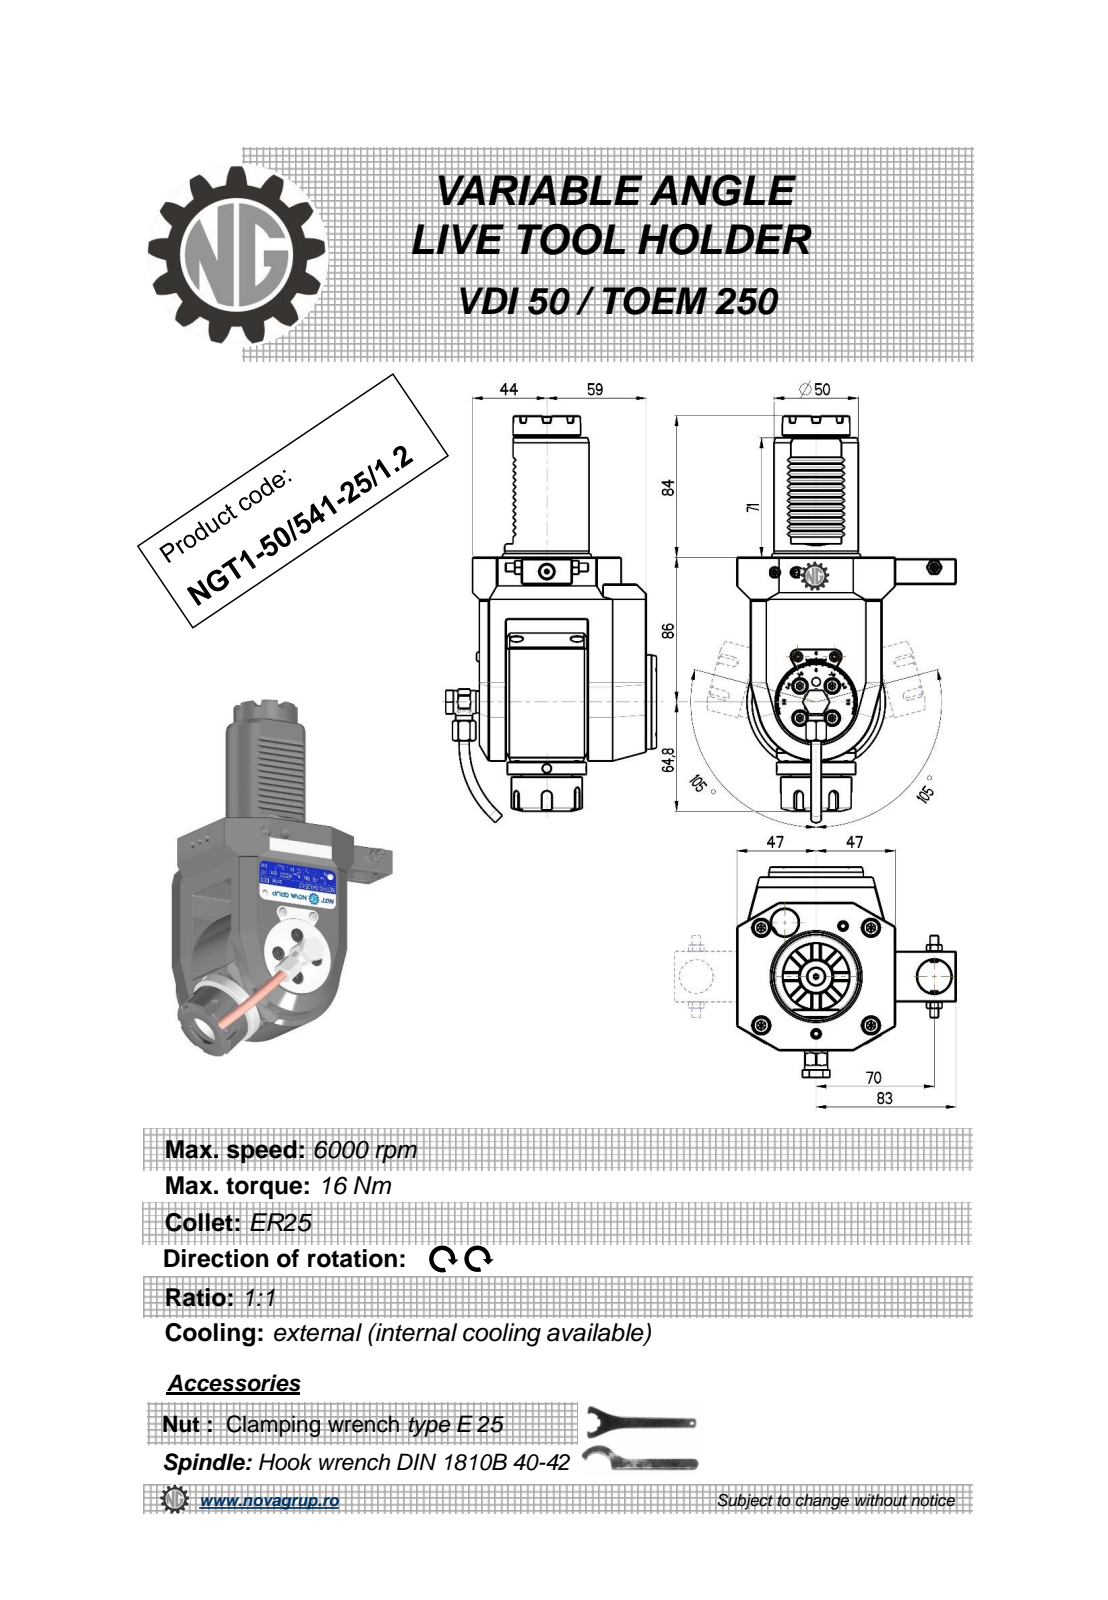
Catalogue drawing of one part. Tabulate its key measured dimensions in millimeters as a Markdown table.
| quantity | value |
| --- | --- |
| part name | NGT1_50_541_25_1_2 |
| STEP written by | PRO/ENGINEER BY PARAMETRIC TECHNOLOGY CORPORATION, 2010280 (CONFIG_CONTROL_DESIGN) |
| units | millimeters |
| bodies | 1 solid, 689 faces (307 planar, 144 cylindrical, 238 other) |
| overall size | 241.67 × 130 × 124.9 |
| volume | 1 022 000 mm³ |
| surface area | 94 158 mm² |
| round holes (diameter × count) | 4 × 3, 5 × 2, 3 × 1, 5.4 × 1, 6.2 × 1, 9 × 1, 9.5 × 1, 10 × 1, 11 × 1, 20 × 1, 20.3 × 1 |
| round bosses / shafts (diameter × count) | 6 × 2, 5.7 × 2, 82 × 1, 56 × 1, 50 × 1, 47 × 1, 42 × 1, 40 × 1 |
| partial cylindrical surfaces (radius × count) | 0.26 × 12, 0.3 × 12, 0.16 × 6, 3 × 5, 0.5 × 4, 1 × 2, 10 × 2, 7.7 × 1 |
| main face-to-face distances | 37, 16, 99, 8, 64, 6, 21, 105, 20, 35 |
| hole center spacings | 0.4, 39.45, 49, 49.4, 70, 85.45, 85.68, 116.95 |
